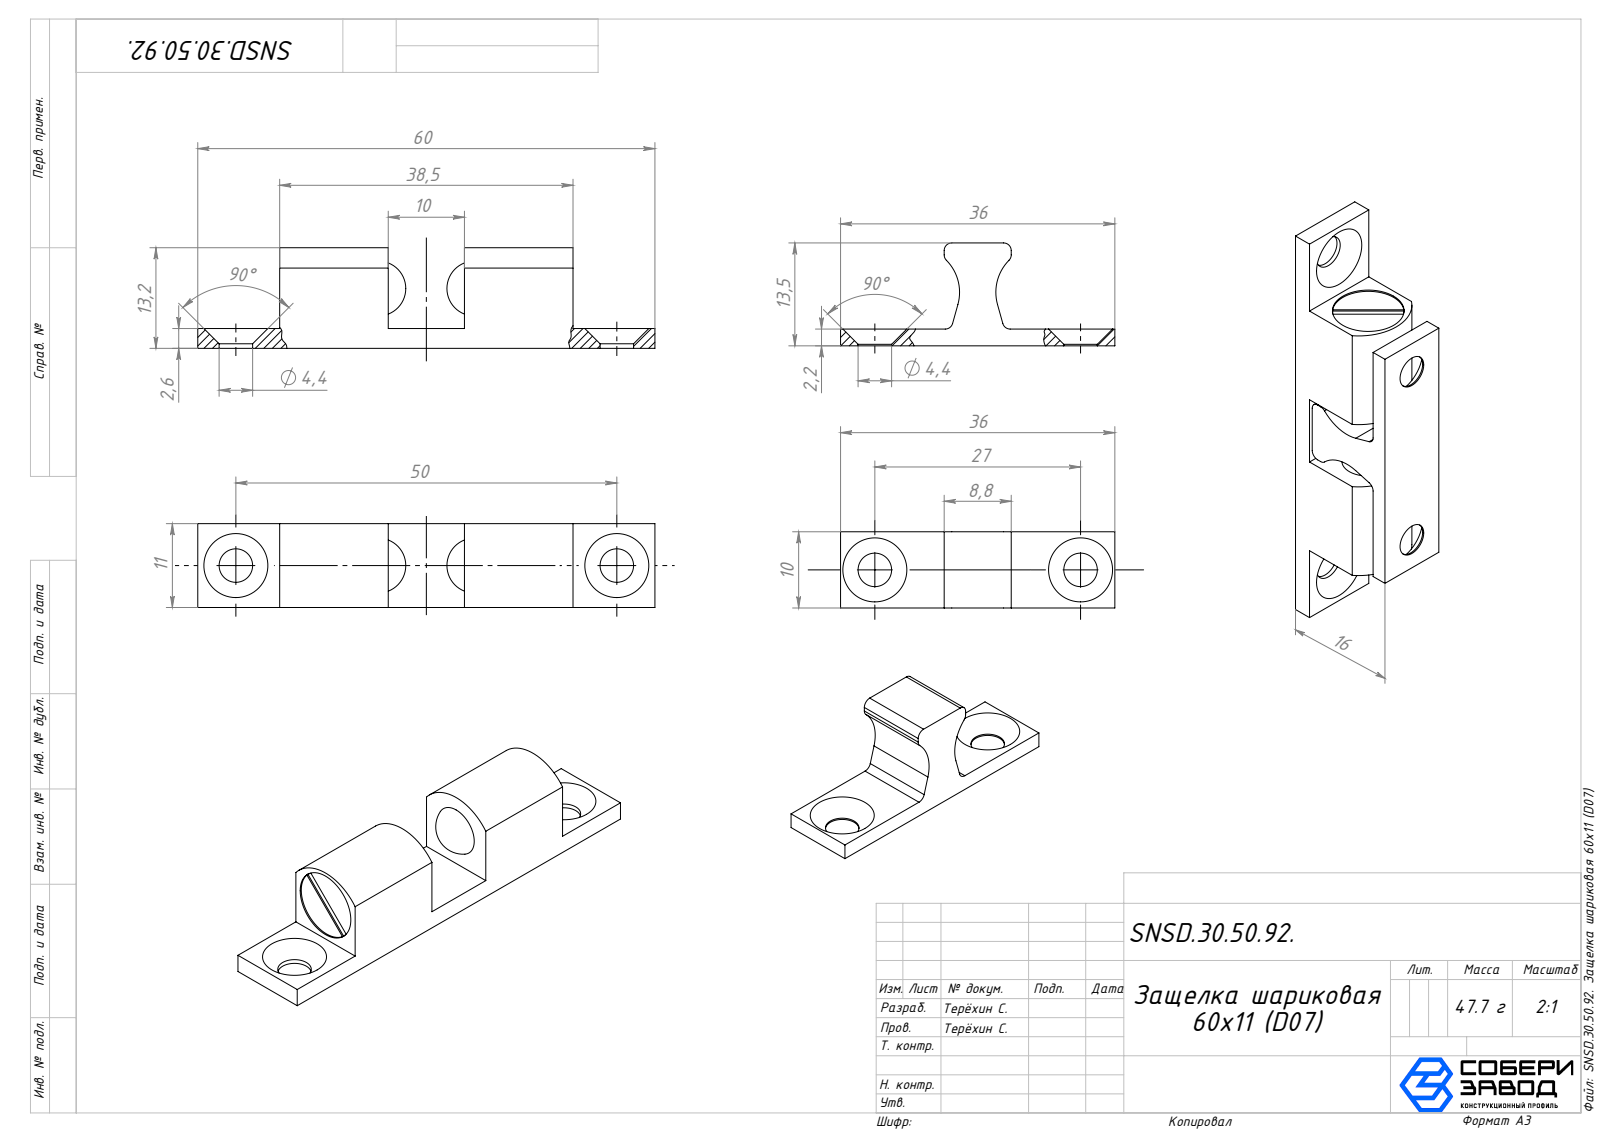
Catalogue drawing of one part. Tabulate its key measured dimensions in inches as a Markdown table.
| quantity | value |
| --- | --- |
| part name | SNSD.30.50.92. Защелка шариковая 60х11 (D07); B66SNSD.30.50.85. Корпус шариков(B59)B62D07_00; B66SNSD.30.50.85. Защелка(B59)B62D07_00 |
| STEP written by | SolidWorks 2025 (AUTOMOTIVE_DESIGN) |
| units | inches |
| bodies | 2 solids, 77 faces (42 planar, 23 cylindrical, 12 other) |
| overall size | 2.362 × 0.634 × 0.433 |
| volume | 0.37 in³ |
| surface area | 6.123 in² |
| round holes (diameter × count) | 0.173 × 4, 0.37 × 1 |
| partial cylindrical surfaces (radius × count) | 0.039 × 6, 0.235 × 2, 0.276 × 1 |
| main face-to-face distances | 0.433, 0.634, 0.102, 0.531, 0.02, 0.413, 0.394, 0.547, 0.445, 0.087 |
| hole center spacings | 0.453, 1.516, 1.063, 1.969 |
